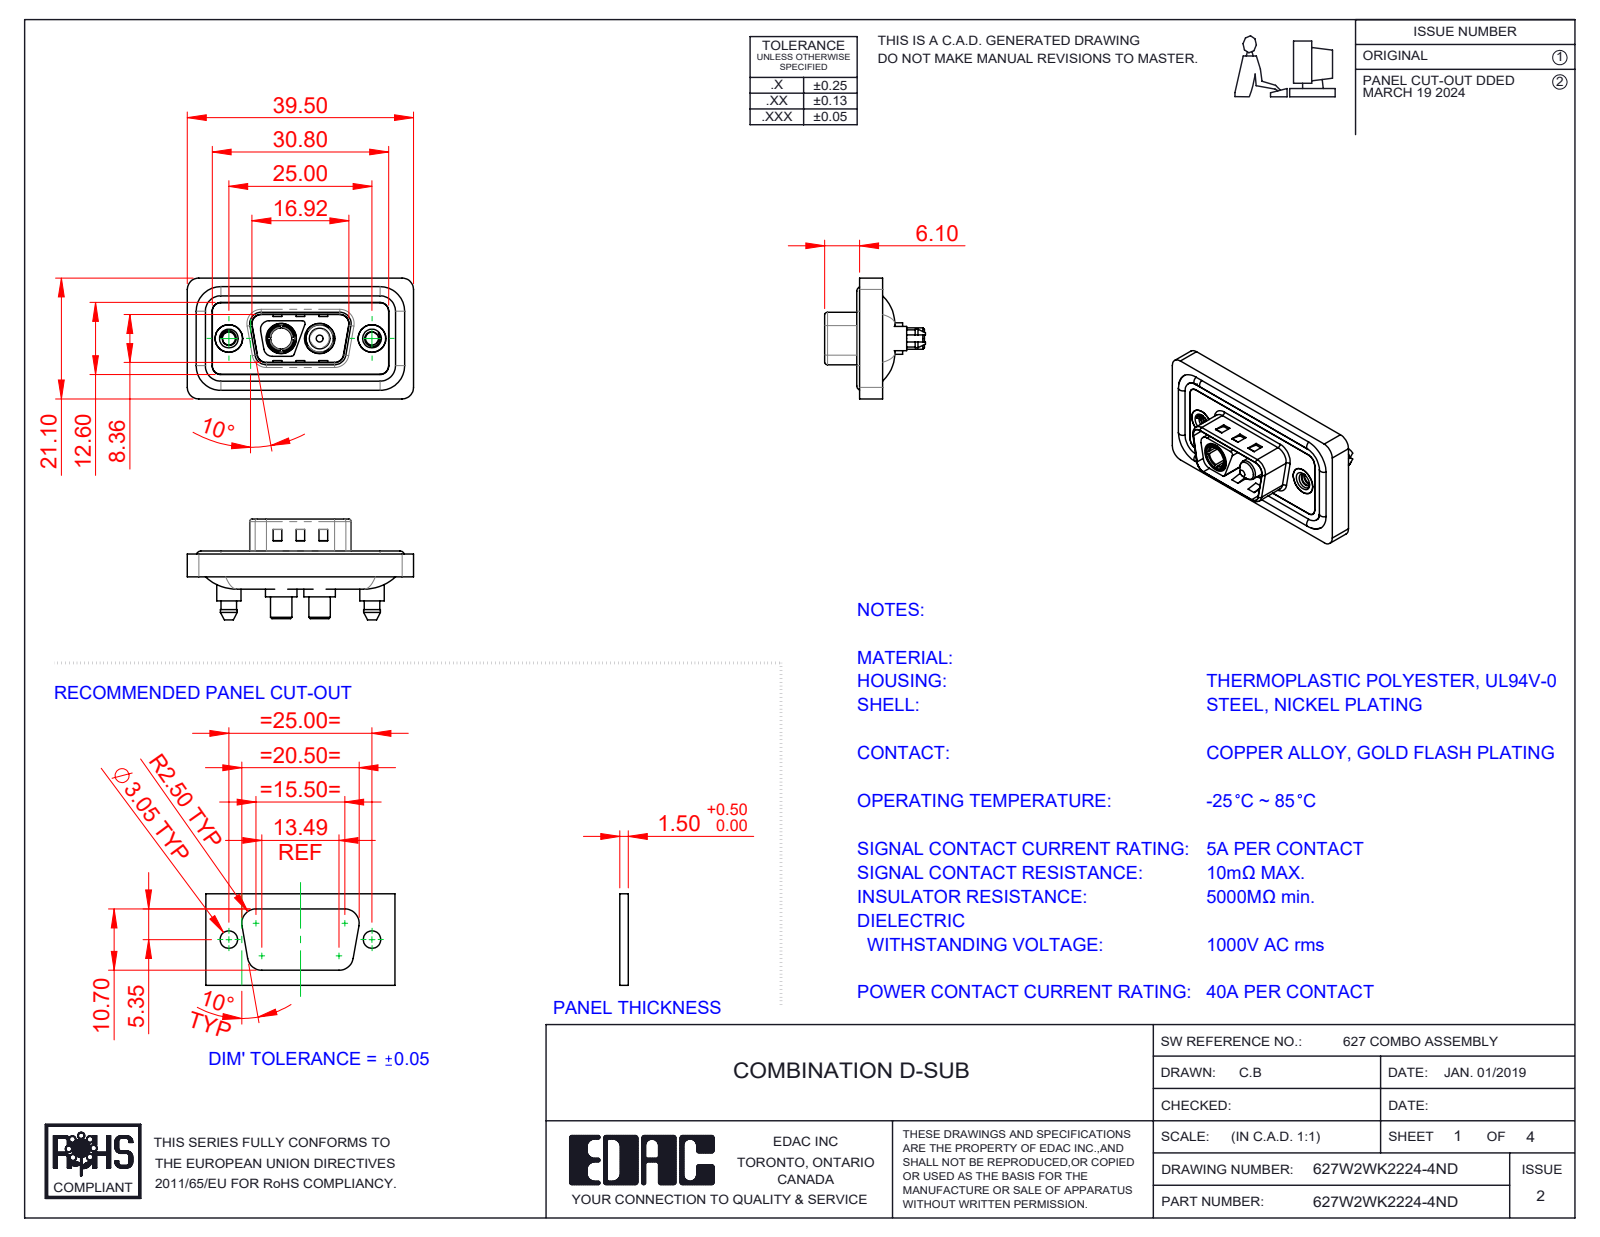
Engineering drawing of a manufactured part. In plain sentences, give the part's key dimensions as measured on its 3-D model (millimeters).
The part is named "627W2WK2224-4ND; 627Combo Shell Front_09 Contacts; 627Combo Shell Rear_09 Contacts; 627Combo Waterproof Housing_09 Contacts (+5 more)". Its 3-D file was written by "SolidWorks 2023 (CONFIG_CONTROL_DESIGN)". It is 11 solids with 592 faces: 205 planar, 267 cylindrical and 120 other. Overall it measures 39.5 by 21.1 by 17.6 millimeters. Its volume is 4 726 cubic millimeters and its surface area 7 700 square millimeters. Round holes: 2 of diameter 2.26, 2 of diameter 4, 2 of diameter 4.8, 2 of diameter 4.85, 2 of diameter 5, 2 of diameter 5.3, 1 of diameter 3.7. Round bosses or shafts: 4 of diameter 1.6, 2 of diameter 5.5, 2 of diameter 5.4, 2 of diameter 5.2, 2 of diameter 4.9, 2 of diameter 4.75, 2 of diameter 4.25, 2 of diameter 3.75. Partial cylindrical surfaces (rounded edges, fillets, slot ends): 26 of radius 1.5, 18 of radius 2, 10 of radius 0.5, 10 of radius 1.6, 4 of radius 0.25, 4 of radius 0.6, 4 of radius 0.65, 4 of radius 0.9. The main face-to-face distances are 0.4, 1.1, 2.9, 3.1, 0.5, 1.6, 1.5, 4, 1.8, 3.2. The hole center spacings are 9.14, 15.86, 6.72, 25.
